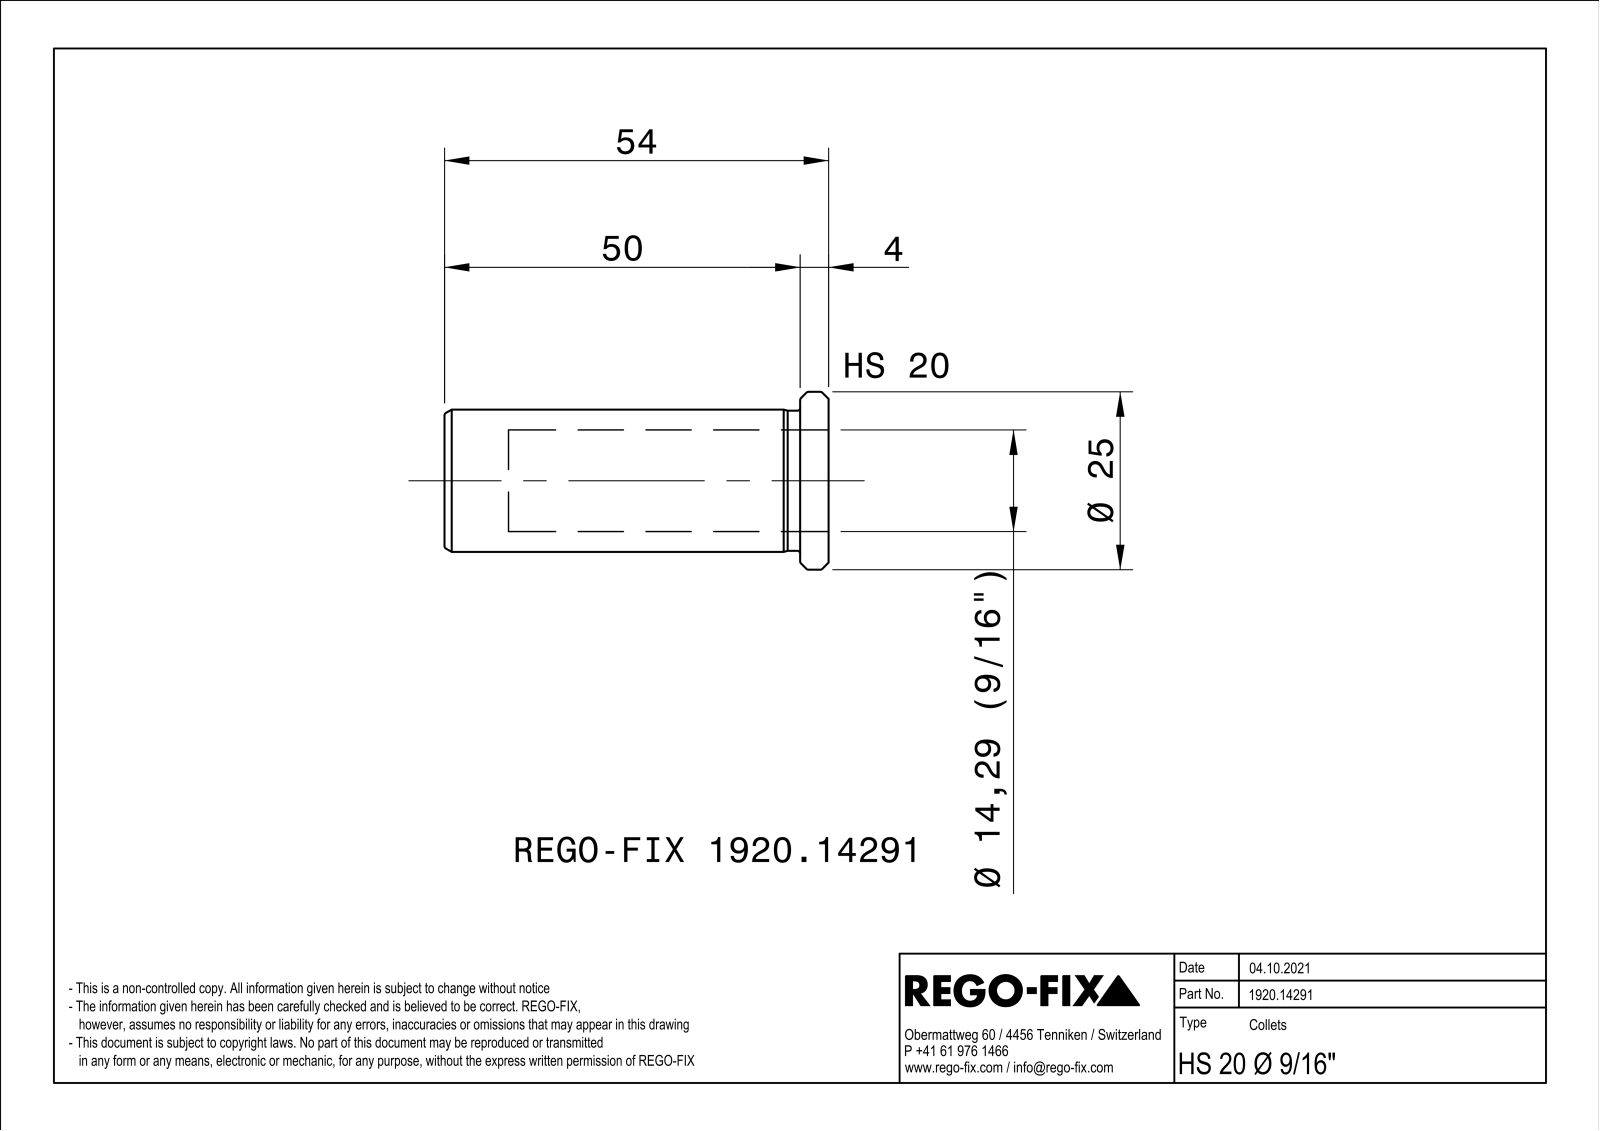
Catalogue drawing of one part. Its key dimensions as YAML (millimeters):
part_name: "NOCUT"
step_written_by: "SIEMENS PLM Software Solid Edge ST10 (AUTOMOTIVE_DESIGN)"
units: millimeters
bodies: {solids: 1, faces: 70, planar: 22, cylindrical: 11, other: 37}
overall_size: [54, 24.98, 24.98]
volume: 8034
surface_area: 7049
round_holes:
  - {diameter: 14.29, count: 1}
  - {diameter: 16.5, count: 1}
round_bosses_or_shafts:
  - {diameter: 25, count: 1}
  - {diameter: 20, count: 1}
  - {diameter: 19.7, count: 1}
face_to_face_distances: [1, 4, 54, 50]
